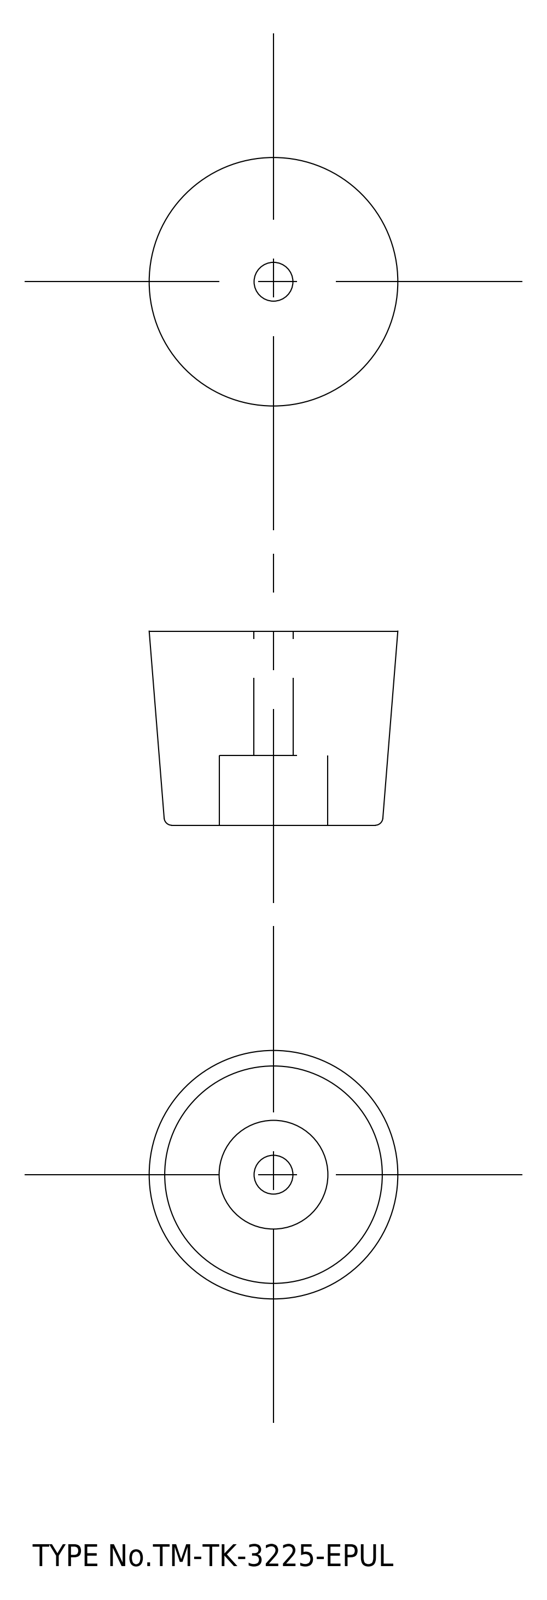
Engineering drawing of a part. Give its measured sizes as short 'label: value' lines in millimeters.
name: washer; rubber foot
written by: spGate 15.6.1 (AUTOMOTIVE_DESIGN)
unit: mm
bodies: 2 solids, 20 faces (6 planar, 10 cylindrical, 4 other)
size: 32 × 32 × 25
volume: 16 018 mm³; area: 4 901 mm²
holes: 1× ⌀5, 1× ⌀14, 1× ⌀16
face distances: 25, 9.8, 15.2, 9, 0.8, 16
